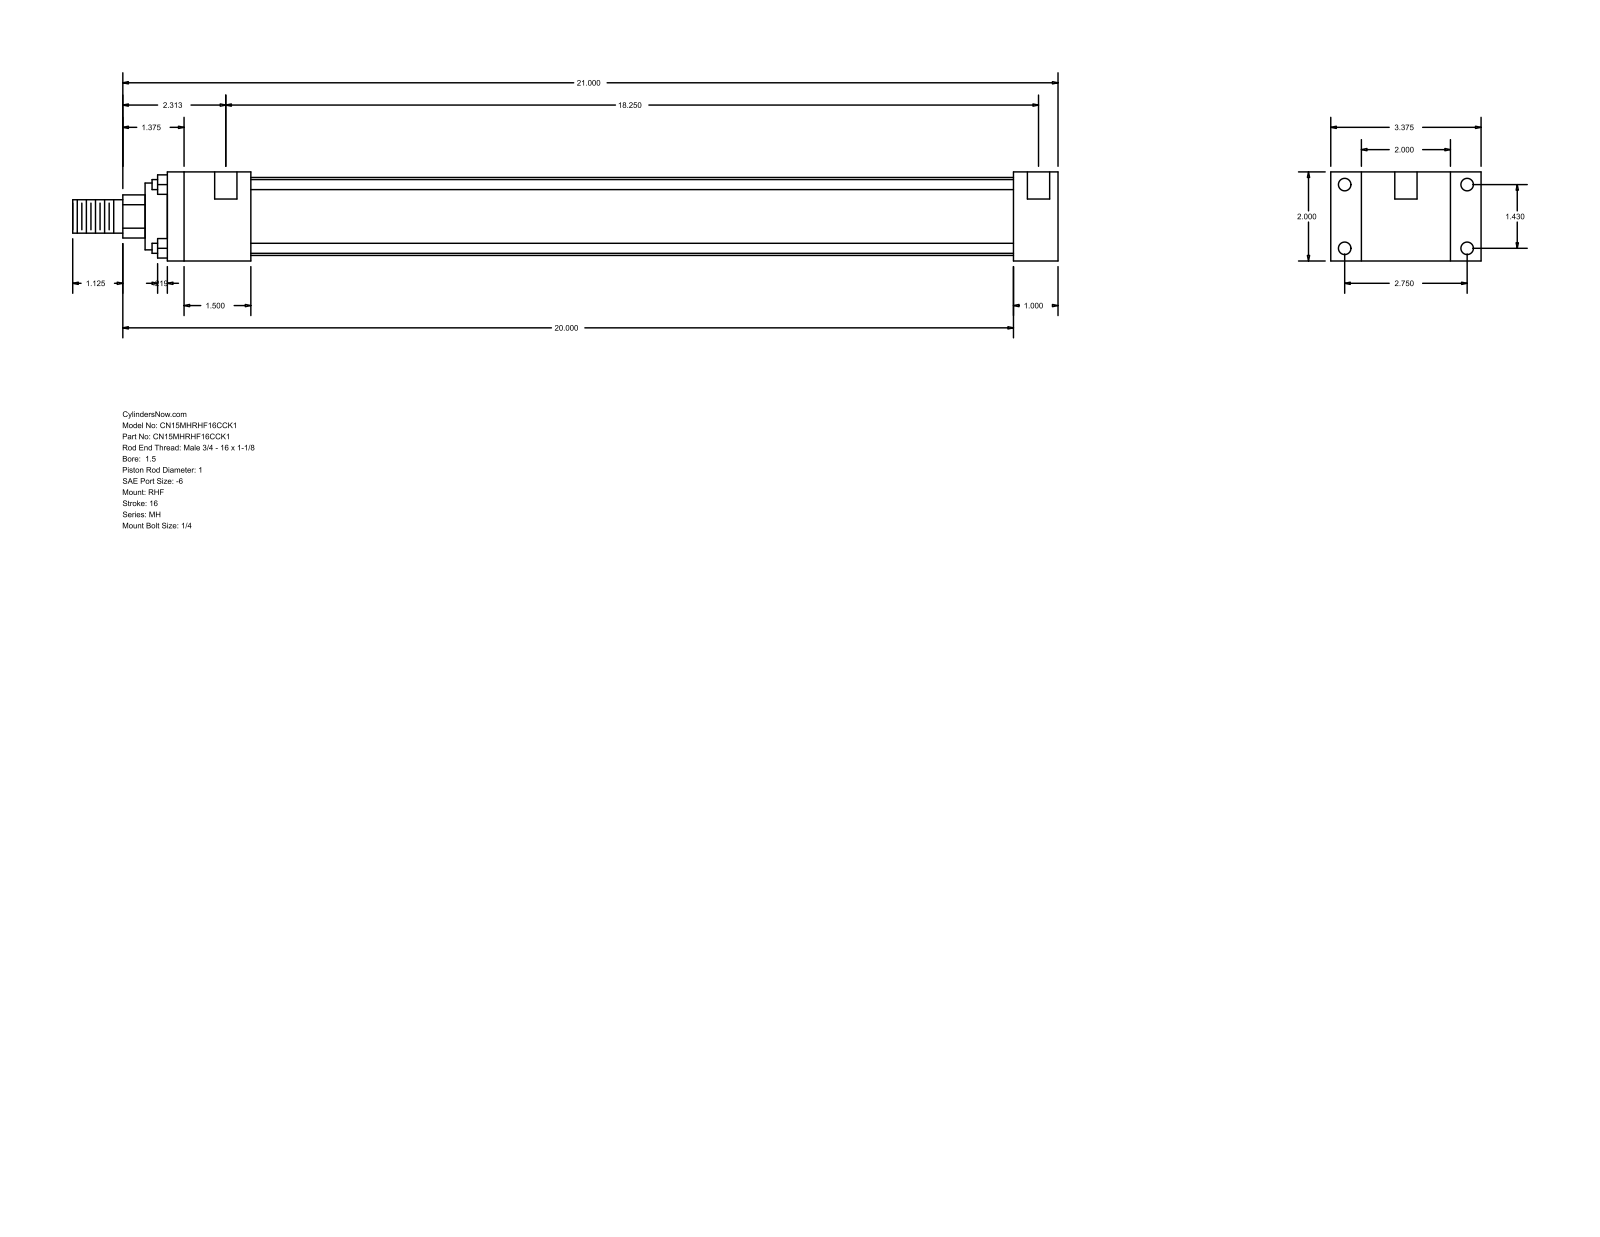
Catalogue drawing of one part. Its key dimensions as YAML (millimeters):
part_name: "MH_RHF__0150_1"
step_written_by: "GSSL Pune (CONFIG_CONTROL_DESIGN)"
units: millimeters
bodies: {solids: 0, faces: 88, planar: 60, cylindrical: 28, other: 0}
overall_size: [561.98, 85.72, 50.8]
round_holes:
  - {diameter: 5.56, count: 4}
  - {diameter: 7.14, count: 4}
  - {diameter: 12.7, count: 2}
round_bosses_or_shafts:
  - {diameter: 5.71, count: 4}
  - {diameter: 44.45, count: 1}
  - {diameter: 38.1, count: 1}
  - {diameter: 25.4, count: 1}
  - {diameter: 19.05, count: 1}
partial_cylinders:
  - {radius: 12.29, count: 1}
face_to_face_distances: [50.8, 25.4, 17.46, 68.26, 85.72, 508, 482.6, 47.63, 434.97, 460.37]
hole_center_spacings: [36.32, 69.84, 78.72, 466.73, 3.18, 463.55]
